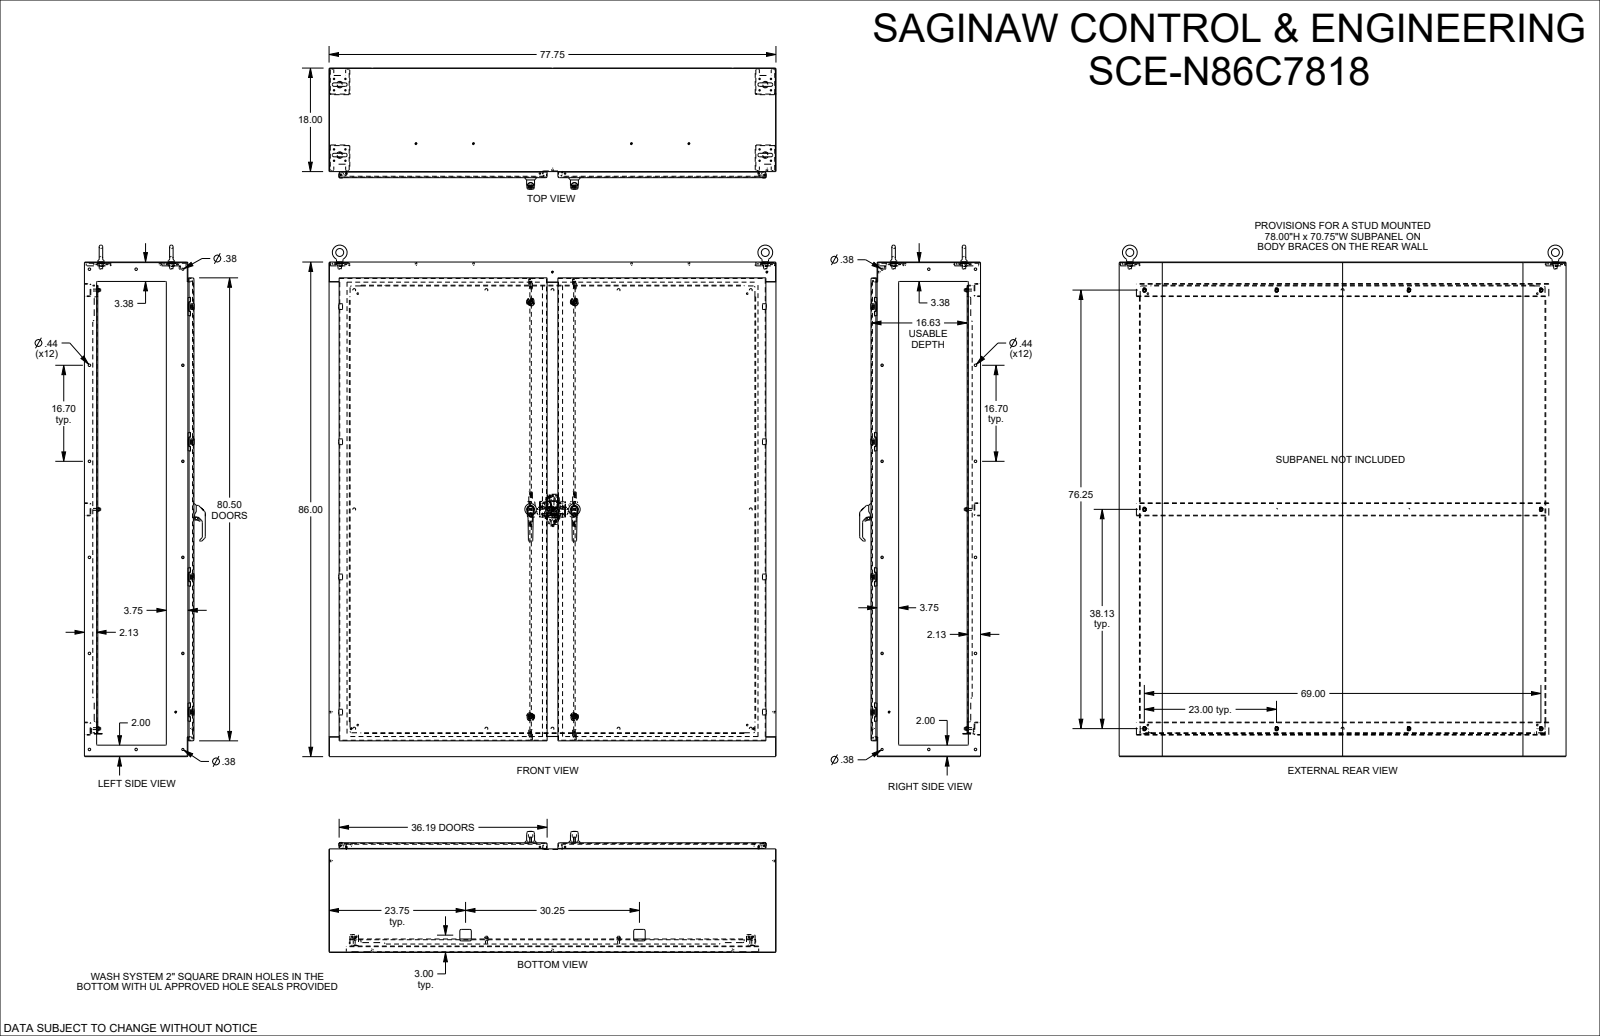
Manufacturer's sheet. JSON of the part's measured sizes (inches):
{"part_name": "SCE-N86C7818", "step_written_by": "SolidWorks 2023 (AUTOMOTIVE_DESIGN)", "units": "inches", "bodies": {"solids": 48, "faces": 7328, "planar": 3022, "cylindrical": 2474, "other": 1832}, "overall_size": [88.945, 77.75, 21.046], "volume_in3": 2135, "surface_area_in2": 40555, "round_holes": [[0.25, 20], [0.375, 18], [0.205, 16], [0.244, 16], [0.437, 12], [0.04, 8], [0.17, 8], [0.218, 8], [0.256, 4], [0.343, 4], [0.344, 4], [0.36, 4]], "round_bosses_or_shafts": [[0.17, 24], [0.25, 20], [0.24, 16], [0.196, 10], [1.4, 4], [1.173, 4], [0.6, 4], [0.341, 4]], "partial_cylinders_radius": [[0.03, 196], [0.015, 166], [0.125, 100], [0.02, 72], [0.02, 48], [0.25, 44], [0.039, 42], [0.04, 40]], "face_to_face_distances": [0.104, 18.954, 19.058, 18.85, 17.896, 1.058, 85.896, 17.792, 1.162, 86], "hole_center_spacings": [23.5, 1.979, 16.7, 23.302, 47, 1.4, 33.4, 37.143]}
